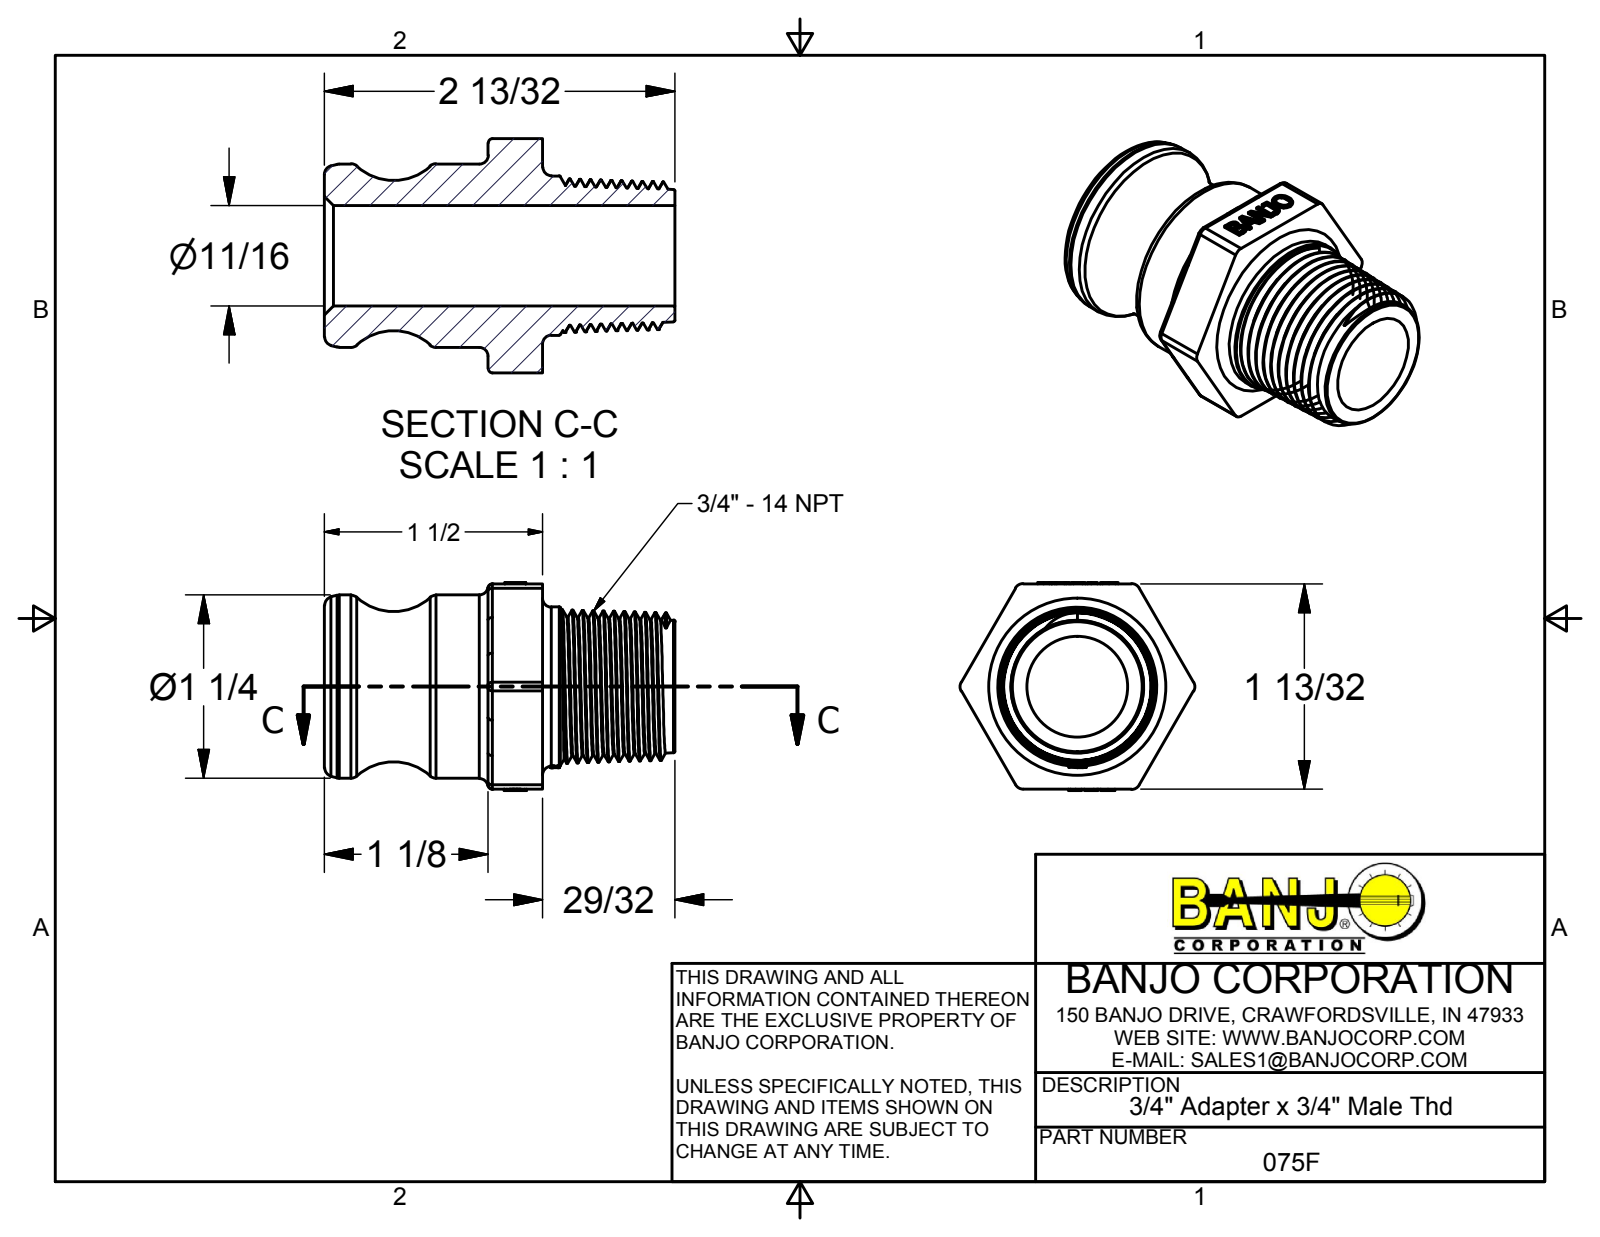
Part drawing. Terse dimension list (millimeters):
name: 075F
written by: Autodesk Inventor 2014 (AUTOMOTIVE_DESIGN)
unit: mm
bodies: 0 solids, 263 faces (102 planar, 31 cylindrical, 130 other)
size: 61.21 × 40.91 × 36.35
holes: 1× ⌀6.95, 1× ⌀17.53
bosses: 1× ⌀32, 1× ⌀27.81
rounds: 6× R0.76, 6× R1.52, 1× R7.06, 1× R14.16
face distances: 35.84, 38.1, 61.21, 23.11, 28.57, 9.53, 32.64, 35.59, 36.09, 0.5
